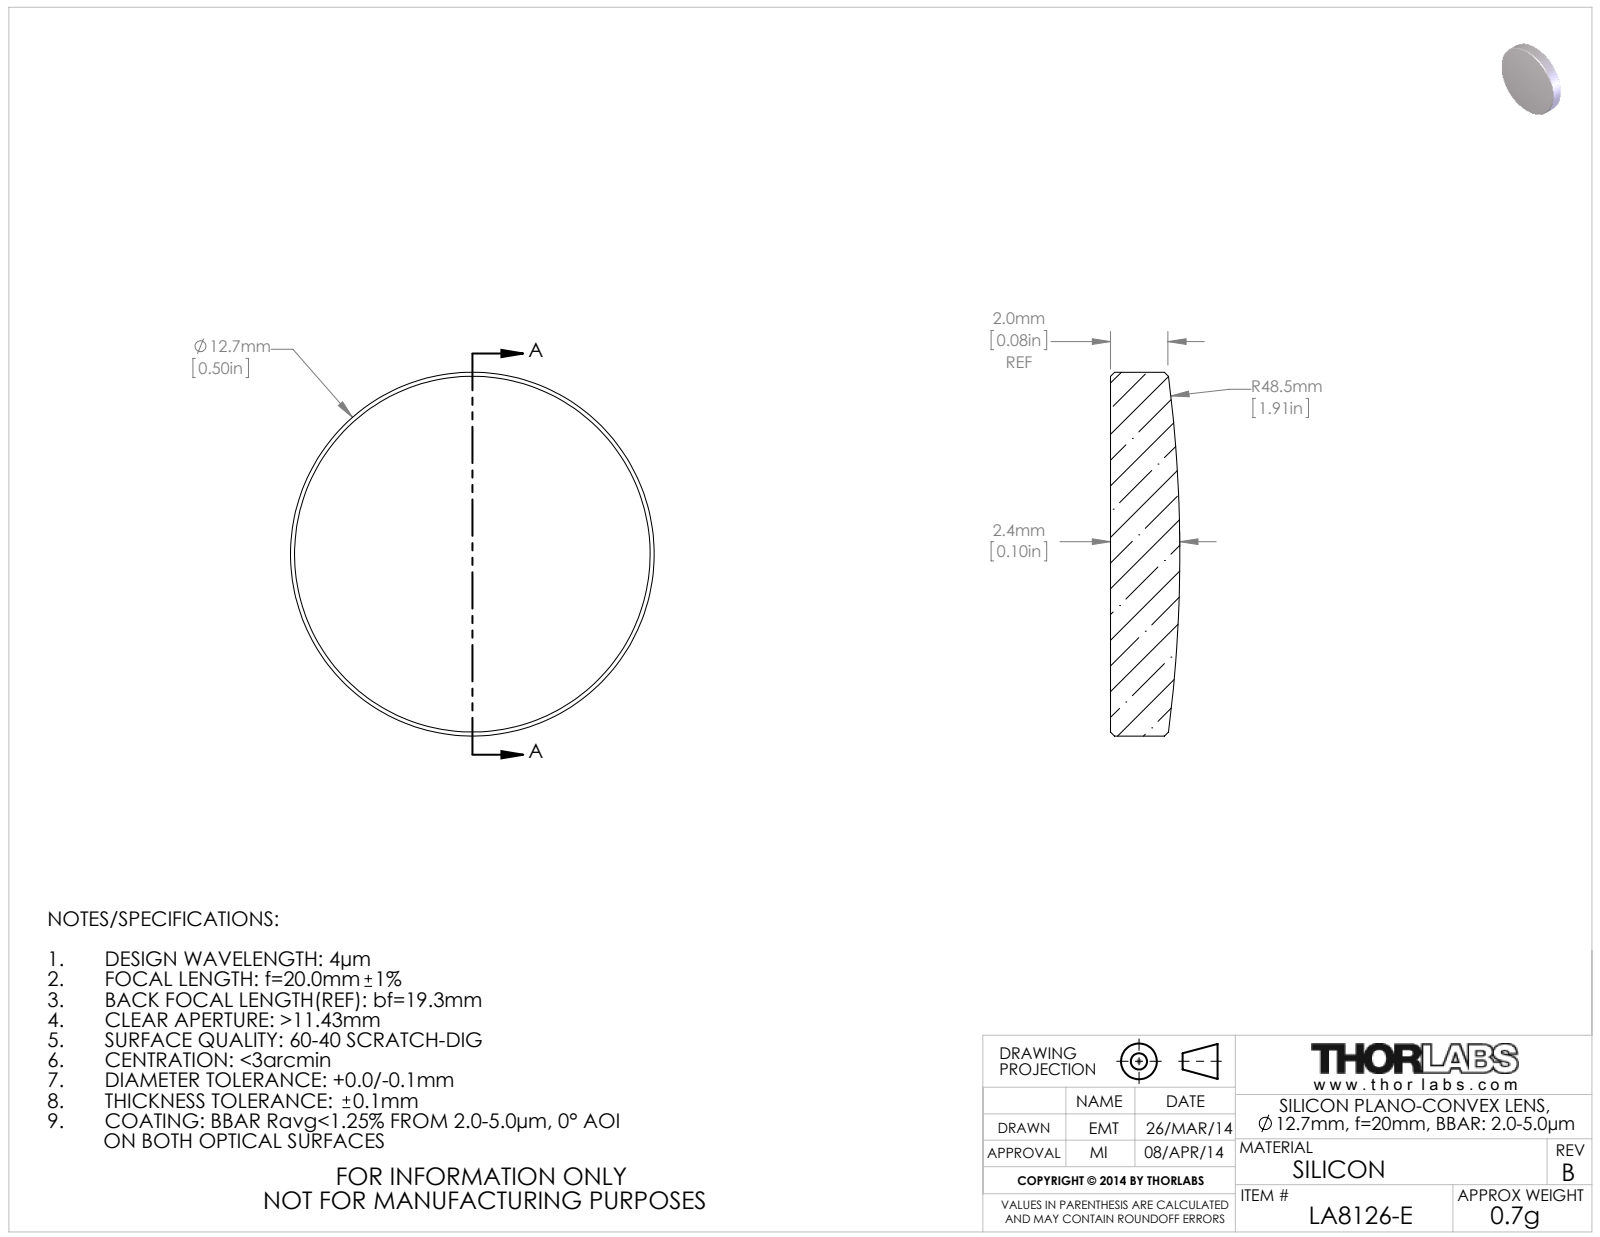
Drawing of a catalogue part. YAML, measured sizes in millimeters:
part_name: "20126-E0W"
step_written_by: "SolidWorks 2014 (CONFIG_CONTROL_DESIGN)"
units: millimeters
bodies: {solids: 1, faces: 9, planar: 1, cylindrical: 2, other: 6}
overall_size: [12.7, 12.7, 2.42]
volume: 279
surface_area: 328
round_bosses_or_shafts:
  - {diameter: 12.7, count: 1}
